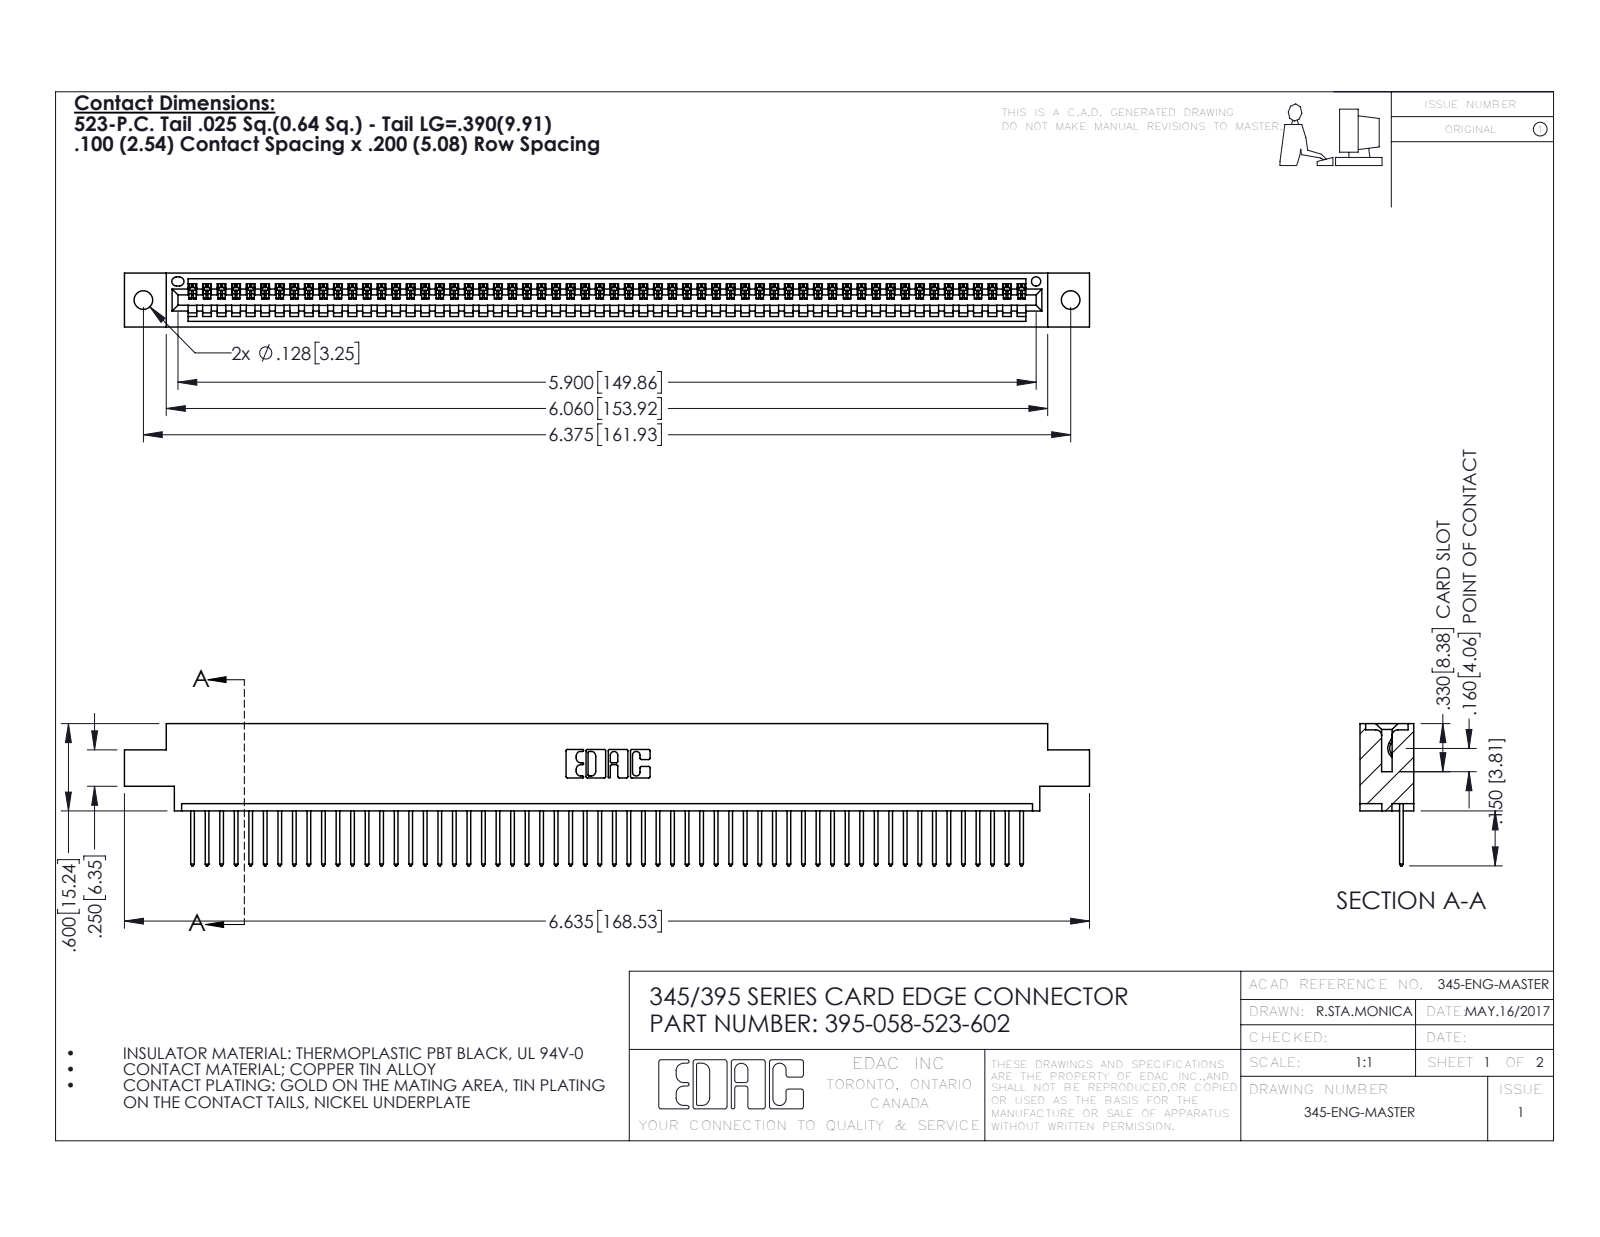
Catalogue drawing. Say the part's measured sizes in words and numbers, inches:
The part is named "345-292-001_345-293-123; 395-058-523-602; 345 Part_0.170 Offset - 0.128 Dia". Its 3-D file was written by "SolidWorks 2016 (CONFIG_CONTROL_DESIGN)". It is 59 solids with 3494 faces: 2404 planar, 1090 cylindrical and 0 other. Overall it measures 6.635 by 0.977 by 0.37 inches. Its volume is 0.974 cubic inches and its surface area 33.1 square inches. Round holes: 2 of diameter 0.128, 1 of diameter 0.064. Partial cylindrical surfaces (rounded edges, fillets, slot ends): 116 of radius 0.006, 116 of radius 0.01, 22 of radius 0.01, 6 of radius 0.007, 6 of radius 0.031, 3 of radius 0.026, 2 of radius 0.031, 2 of radius 0.04. The main face-to-face distances are 0.298, 0.072, 0.37, 0.098, 0.272, 0.025, 0.2, 0.225, 0.175, 0.149. The hole center spacings are 0.27, 6.139, 6.375.
